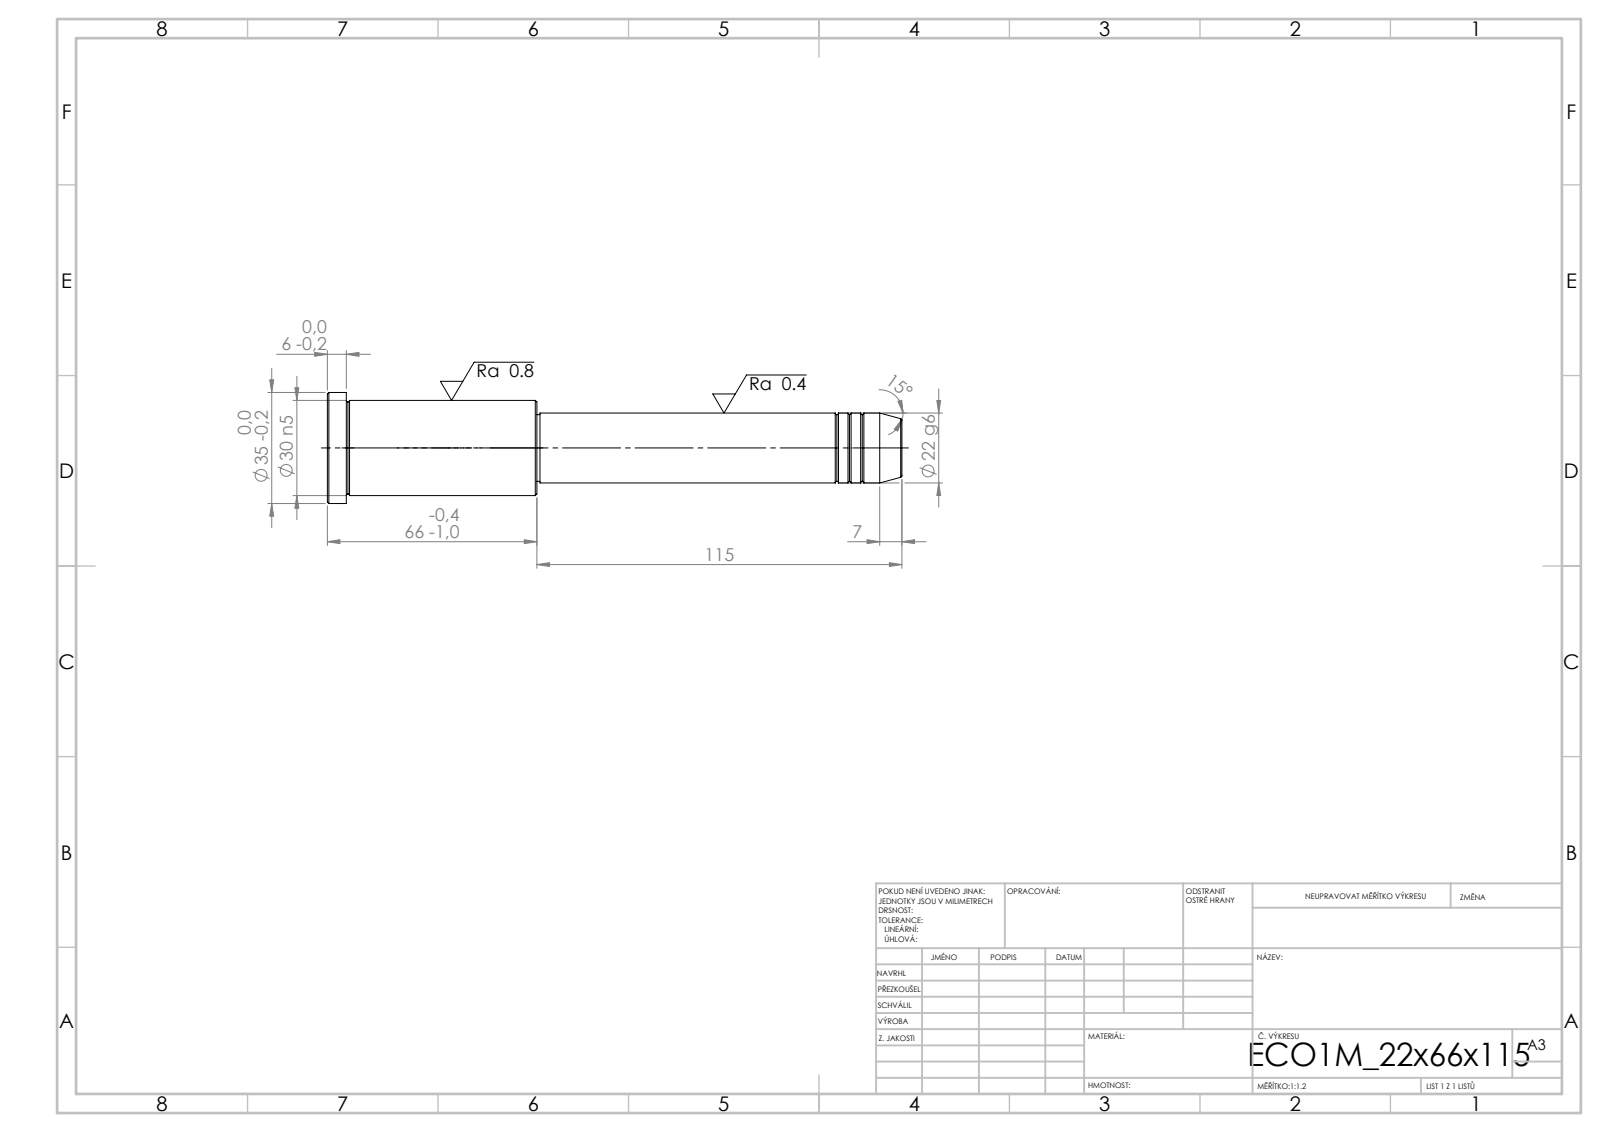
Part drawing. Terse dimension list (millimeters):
written by: SolidWorks 2019 (CONFIG_CONTROL_DESIGN)
unit: mm
bodies: 1 solid, 43 faces (5 planar, 14 cylindrical, 24 other)
size: 181 × 35 × 35
volume: 91 295 mm³; area: 16 200 mm²
bosses: 1× ⌀35, 1× ⌀30, 1× ⌀22, 1× ⌀21
face distances: 66, 60, 6, 115, 175, 181, 114, 1, 61, 67
